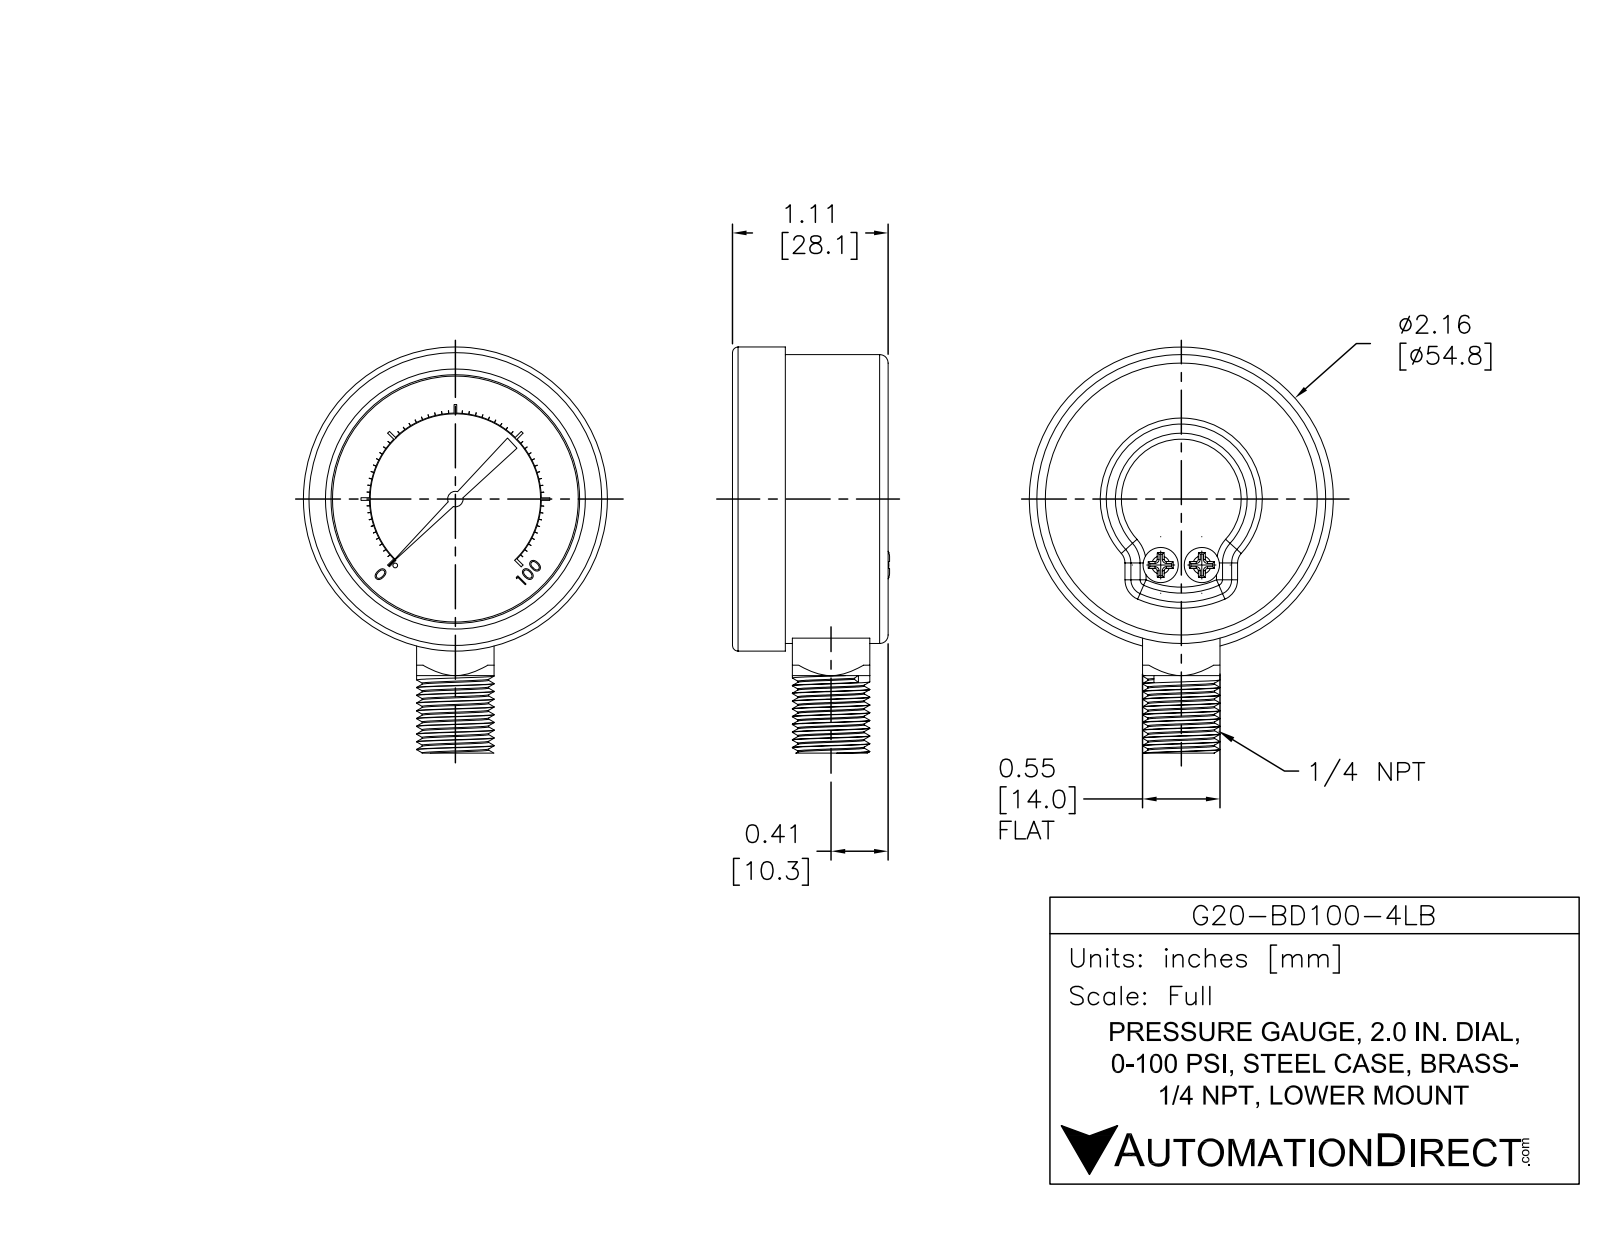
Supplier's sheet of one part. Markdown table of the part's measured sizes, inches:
| quantity | value |
| --- | --- |
| part name | G20-BD100-4LB |
| STEP written by | SolidWorks 2021 (AUTOMOTIVE_DESIGN) |
| units | inches |
| bodies | 1 solid, 420 faces (274 planar, 81 cylindrical, 65 other) |
| overall size | 2.882 × 2.158 × 1.115 |
| volume | 3.182 in³ |
| surface area | 18.02 in² |
| round holes (diameter × count) | 0.14 × 1, 1.745 × 1 |
| round bosses / shafts (diameter × count) | 0.25 × 2, 2.158 × 1, 2.05 × 1, 0.55 × 1, 0.11 × 1, 0.033 × 1 |
| partial cylindrical surfaces (radius × count) | 0.06 × 4, 0.605 × 1, 0.61 × 1 |
| main face-to-face distances | 0.815, 1.105, 0.29, 0.1, 0.715, 1.005, 0.63, 0.73, 0.085, 0.375 |
